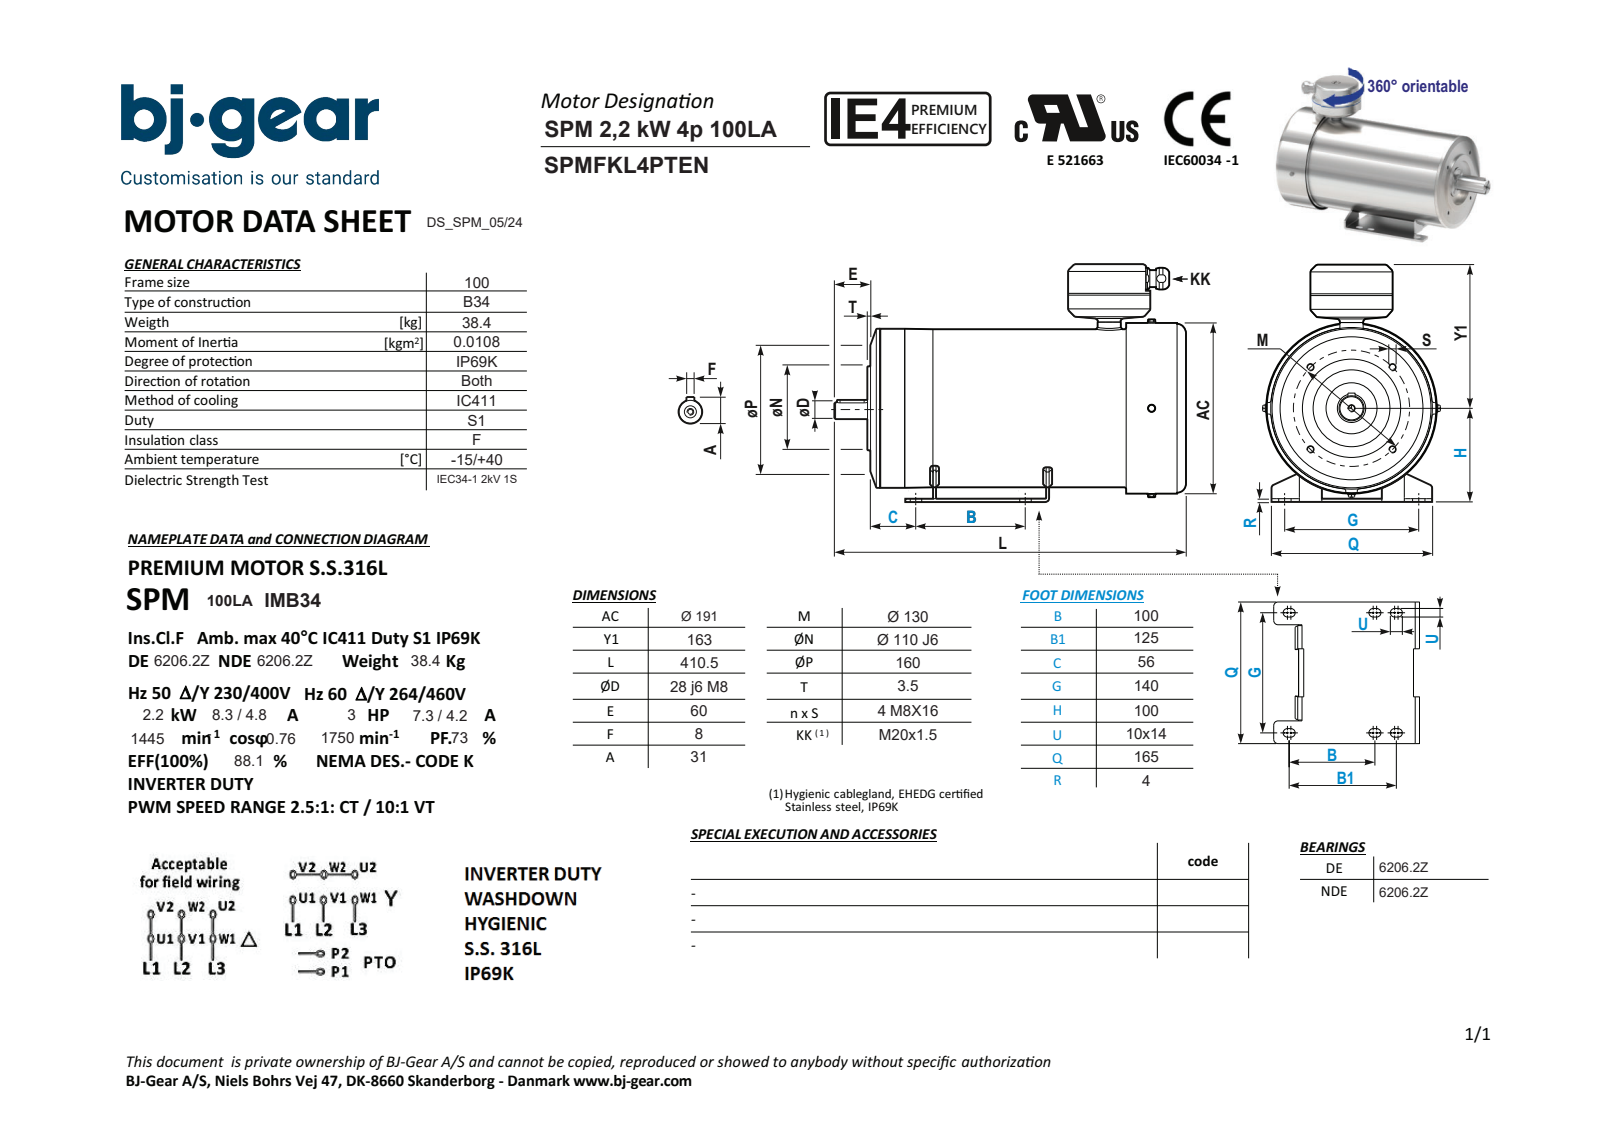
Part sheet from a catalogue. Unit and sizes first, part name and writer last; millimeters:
Units: millimetres
Overall size (bounding box): 410.5 × 262 × 199
Round holes (diameter × count): ⌀6.65 ×4, ⌀4.92 ×1, ⌀7 ×1, ⌀8.4 ×1, ⌀13.4 ×1, ⌀16 ×1, ⌀85 ×1
Round bosses / shafts (diameter × count): ⌀9 ×2, ⌀191 ×1, ⌀178 ×1, ⌀177.98 ×1, ⌀110 ×1, ⌀93 ×1, ⌀84 ×1, ⌀30 ×1
Partial cylindrical surfaces — rounded edges, fillets, slot ends (radius × count): R5 ×18, R3 ×6, R1 ×4, R4 ×4, R12.8 ×1, R88.5 ×1
Main face-to-face distances: 4, 350.5, 6, 344.5, 262, 258, 67, 3, 277.5, 283.5
Hole centre spacings: 65, 91.92, 110.55, 129.99, 197.87, 146.5
Volume: 9 457 000 mm³ · Surface area: 350 638 mm²
Bodies: 2 solids, 288 faces (121 planar, 103 cylindrical, 64 other)
Part name (STEP PRODUCT): SPMFKL4PTEVN4KFU1-N---NNN; SPMFKL4JTEVN4KFU1-N---NNN; SPM909022
STEP written by: Solid Edge (AUTOMOTIVE_DESIGN)
